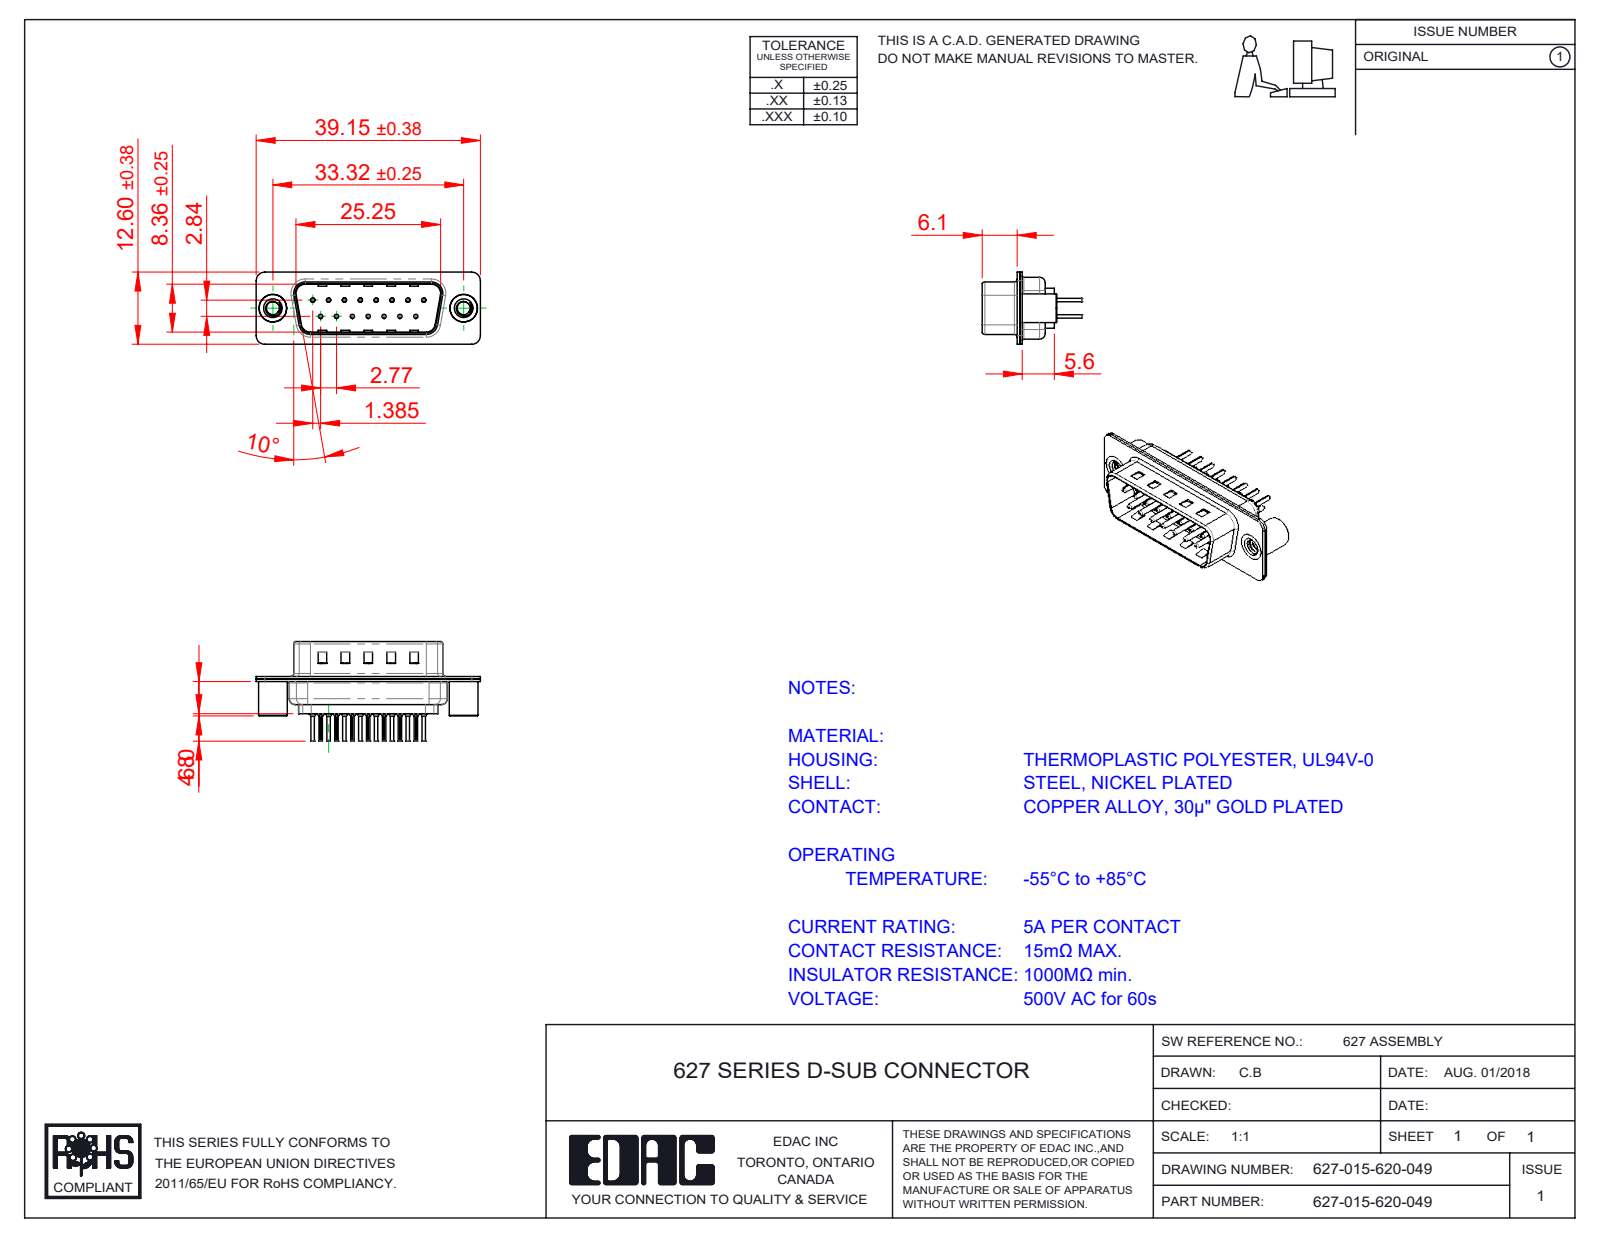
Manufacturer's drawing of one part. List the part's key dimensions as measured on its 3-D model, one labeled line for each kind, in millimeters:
Part name (STEP PRODUCT): 627 4-40 Threaded Standoff BS; 627-015-620-049; 627 Contact Row 2_20L; 627 Shell Front_15 Contacts (+3 more)
STEP written by: SolidWorks 2020 (CONFIG_CONTROL_DESIGN)
Units: millimetres
Bodies: 20 solids, 1832 faces (499 planar, 708 cylindrical, 625 other)
Overall size (bounding box): 39.15 × 17.3 × 12.6
Volume: 1 927 mm³ · Surface area: 5 583 mm²
Round holes (diameter × count): ⌀0.2 ×15, ⌀0.35 ×15, ⌀1.1 ×15, ⌀1.6 ×15, ⌀2.26 ×2, ⌀4 ×2, ⌀4.8 ×2
Round bosses / shafts (diameter × count): ⌀2 ×15, ⌀1.5 ×15, ⌀0.75 ×15, ⌀0.6 ×15, ⌀5 ×2, ⌀4.9 ×2
Partial cylindrical surfaces — rounded edges, fillets, slot ends (radius × count): R0.1 ×30, R1.5 ×16, R2 ×12, R0.5 ×8, R1.6 ×8, R0.25 ×4, R0.6 ×4, R0.65 ×4
Main face-to-face distances: 0.4, 0.45, 0.9, 0.82, 9.58, 8.76, 1.5, 1.4, 6.5, 5.6
Hole centre spacings: 3.16, 2.77, 5.54, 8.31, 11.08, 5.03, 5.04, 7.48
